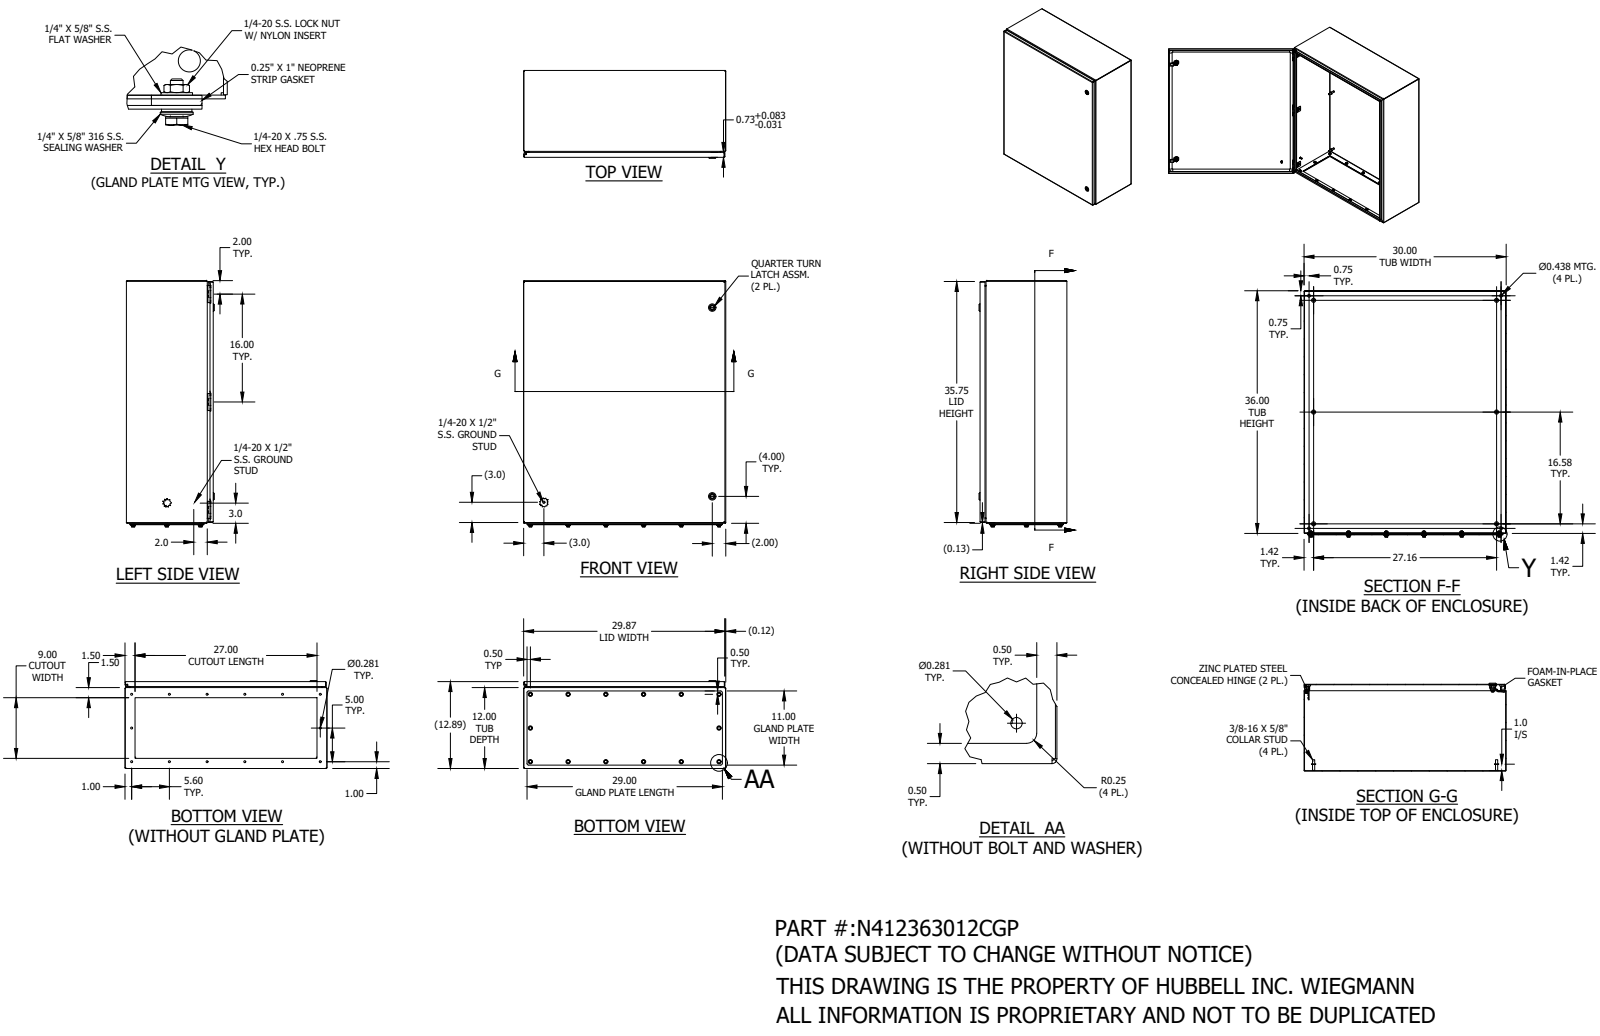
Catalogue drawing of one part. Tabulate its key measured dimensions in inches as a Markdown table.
| quantity | value |
| --- | --- |
| part name | N412363012CGP |
| STEP written by | SolidWorks 2019 (AUTOMOTIVE_DESIGN) |
| units | inches |
| bodies | 115 solids, 3255 faces (1273 planar, 1000 cylindrical, 982 other) |
| overall size | 36.519 × 30 × 13.044 |
| volume | 341.5 in³ |
| surface area | 8 667 in² |
| round holes (diameter × count) | 0.281 × 16, 0.211 × 14, 0.29 × 14, 0.16 × 12, 0.35 × 9, 0.275 × 8, 0.188 × 7, 0.235 × 7, 0.235 × 7, 0.093 × 6, 0.167 × 6, 0.275 × 6 |
| round bosses / shafts (diameter × count) | 0.25 × 28, 0.625 × 18, 0.65 × 14, 0.6 × 14, 0.438 × 14, 0.36 × 6, 0.33 × 6, 0.32 × 6 |
| partial cylindrical surfaces (radius × count) | 0.012 × 56, 0.05 × 38, 0.02 × 21, 0.047 × 20, 0.121 × 20, 0.125 × 12, 0.13 × 12, 0.157 × 9 |
| main face-to-face distances | 0.074, 12.812, 12.738, 12.886, 0.074, 29.926, 36.13, 29.852, 30, 36.056 |
| hole center spacings | 5, 5.6, 16, 10, 11.2, 11.461, 0.66, 7.507 |
